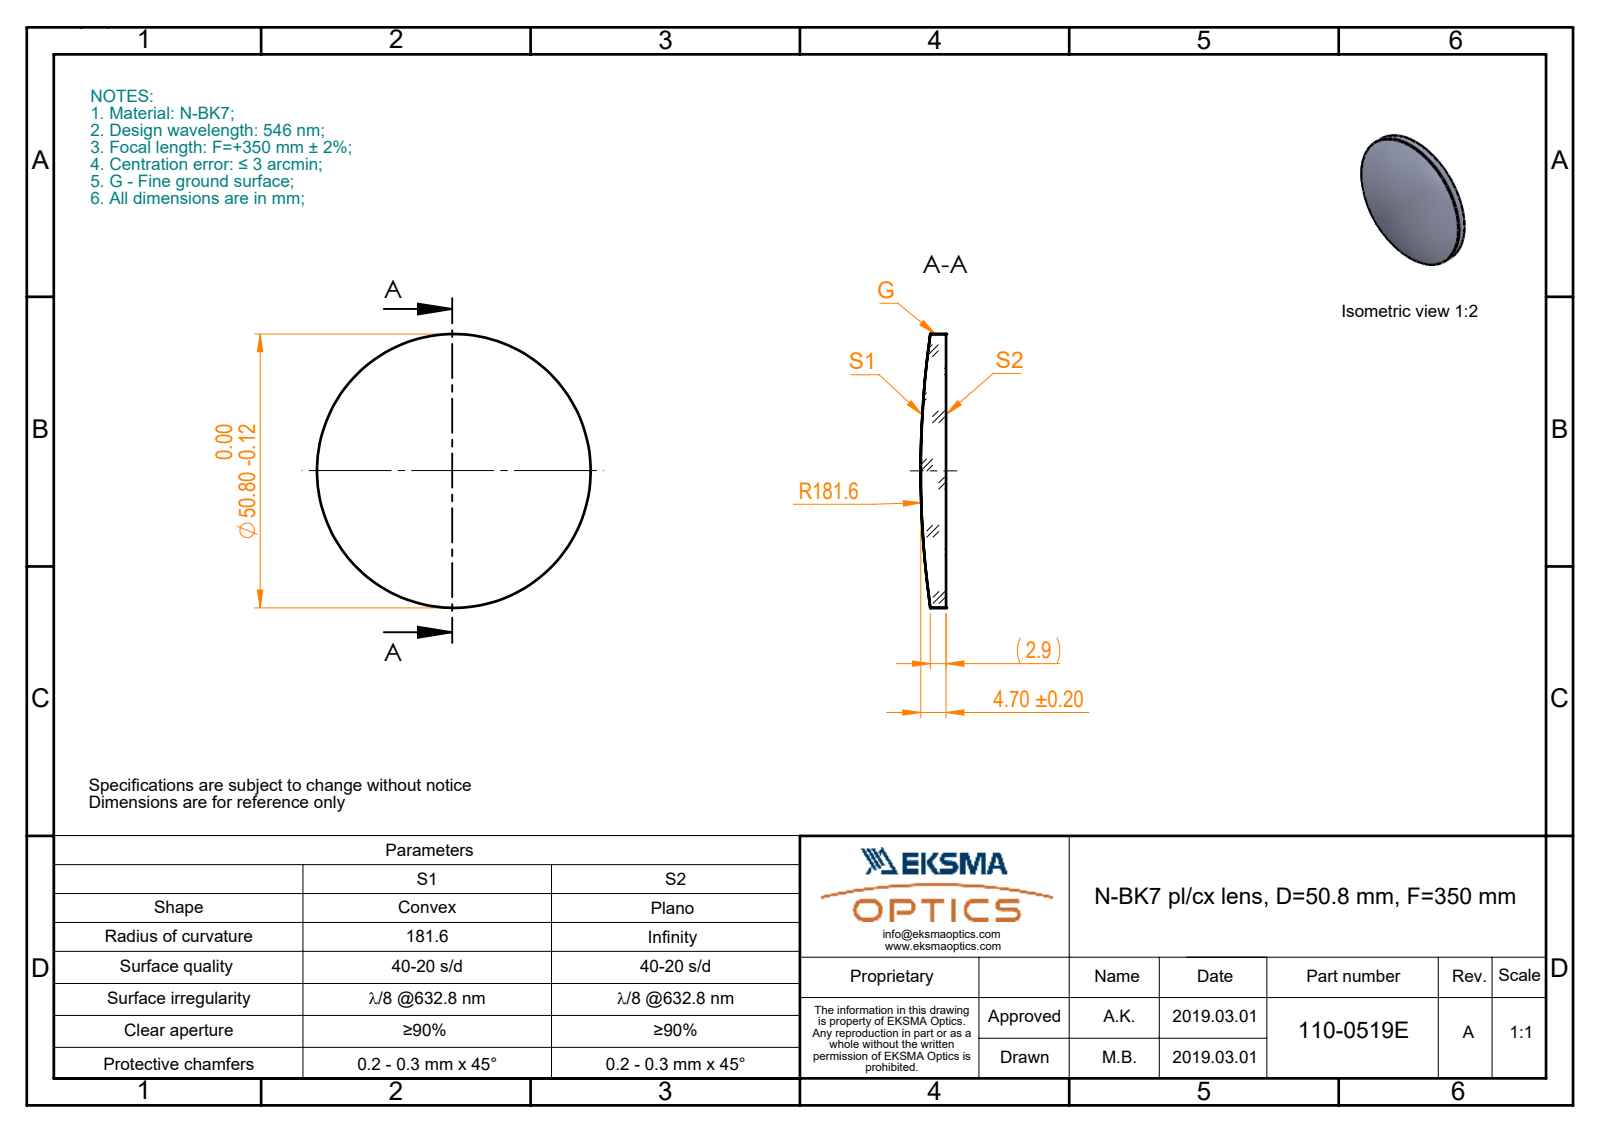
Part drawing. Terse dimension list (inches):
name: 110-0519E BK7 pl-cx 50.8 F350
written by: SolidWorks 2017 (CONFIG_CONTROL_DESIGN)
unit: in
bodies: 1 solid, 5 faces (1 planar, 2 cylindrical, 2 other)
size: 2 × 2 × 0.185
volume: 0.471 in³; area: 7.02 in²
bosses: 1× ⌀2
